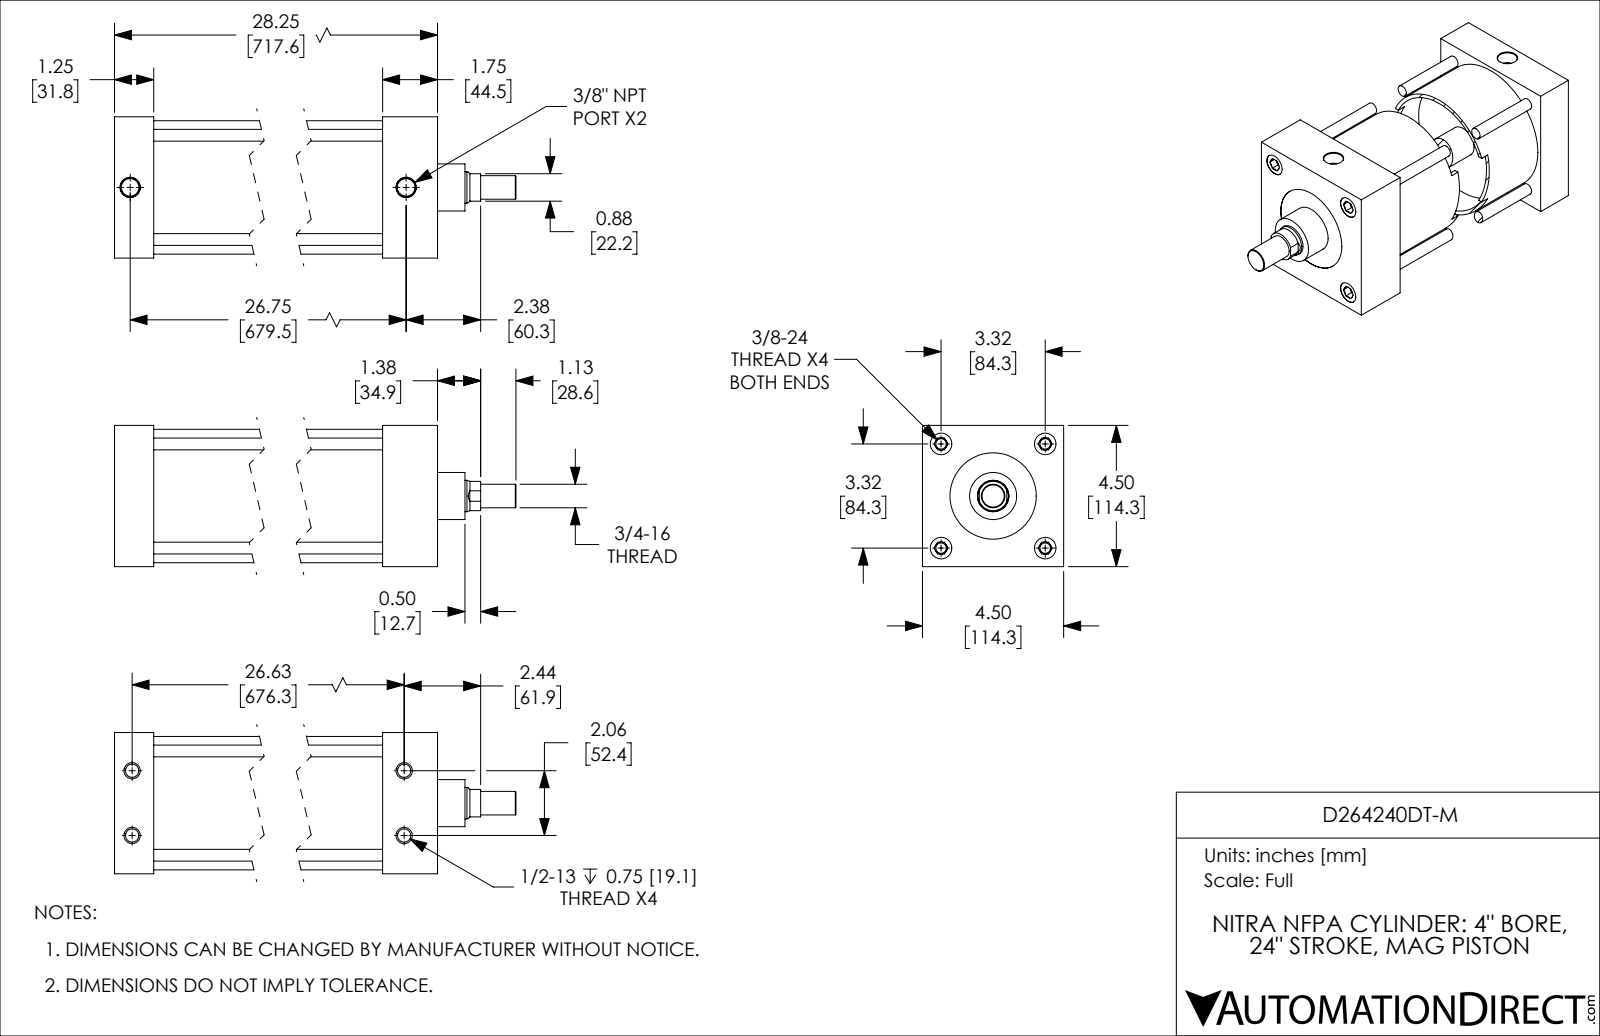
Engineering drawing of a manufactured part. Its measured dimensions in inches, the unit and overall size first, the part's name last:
Units: inches
Overall size (bounding box): 30.75 × 4.5 × 4.5
Round holes (diameter × count): ⌀0.332 ×4, ⌀0.422 ×4, ⌀0.687 ×4, ⌀0.562 ×2, ⌀1.001 ×1, ⌀2.75 ×1, ⌀4.001 ×1
Round bosses / shafts (diameter × count): ⌀0.375 ×4, ⌀4.251 ×1, ⌀3.999 ×1, ⌀1.5 ×1, ⌀0.999 ×1, ⌀0.75 ×1
Partial cylindrical surfaces — rounded edges, fillets, slot ends (radius × count): R0.469 ×1
Main face-to-face distances: 1.25, 4.5, 26.5, 25.25, 28.25, 27, 1.75, 2.5, 24, 25.75
Hole centre spacings: 2.347, 3.32, 26.707, 1.033, 4.695, 26.625, 26.705, 1.034
Volume: 147.3 in³ · Surface area: 1 064 in²
Bodies: 2 solids, 198 faces (58 planar, 62 cylindrical, 78 other)
Part name (STEP PRODUCT): D264240DT-M_BODY; D264240DT-M_PISTON_KK1; D264240DT-M
STEP written by: SolidWorks 2019 (CONFIG_CONTROL_DESIGN)
